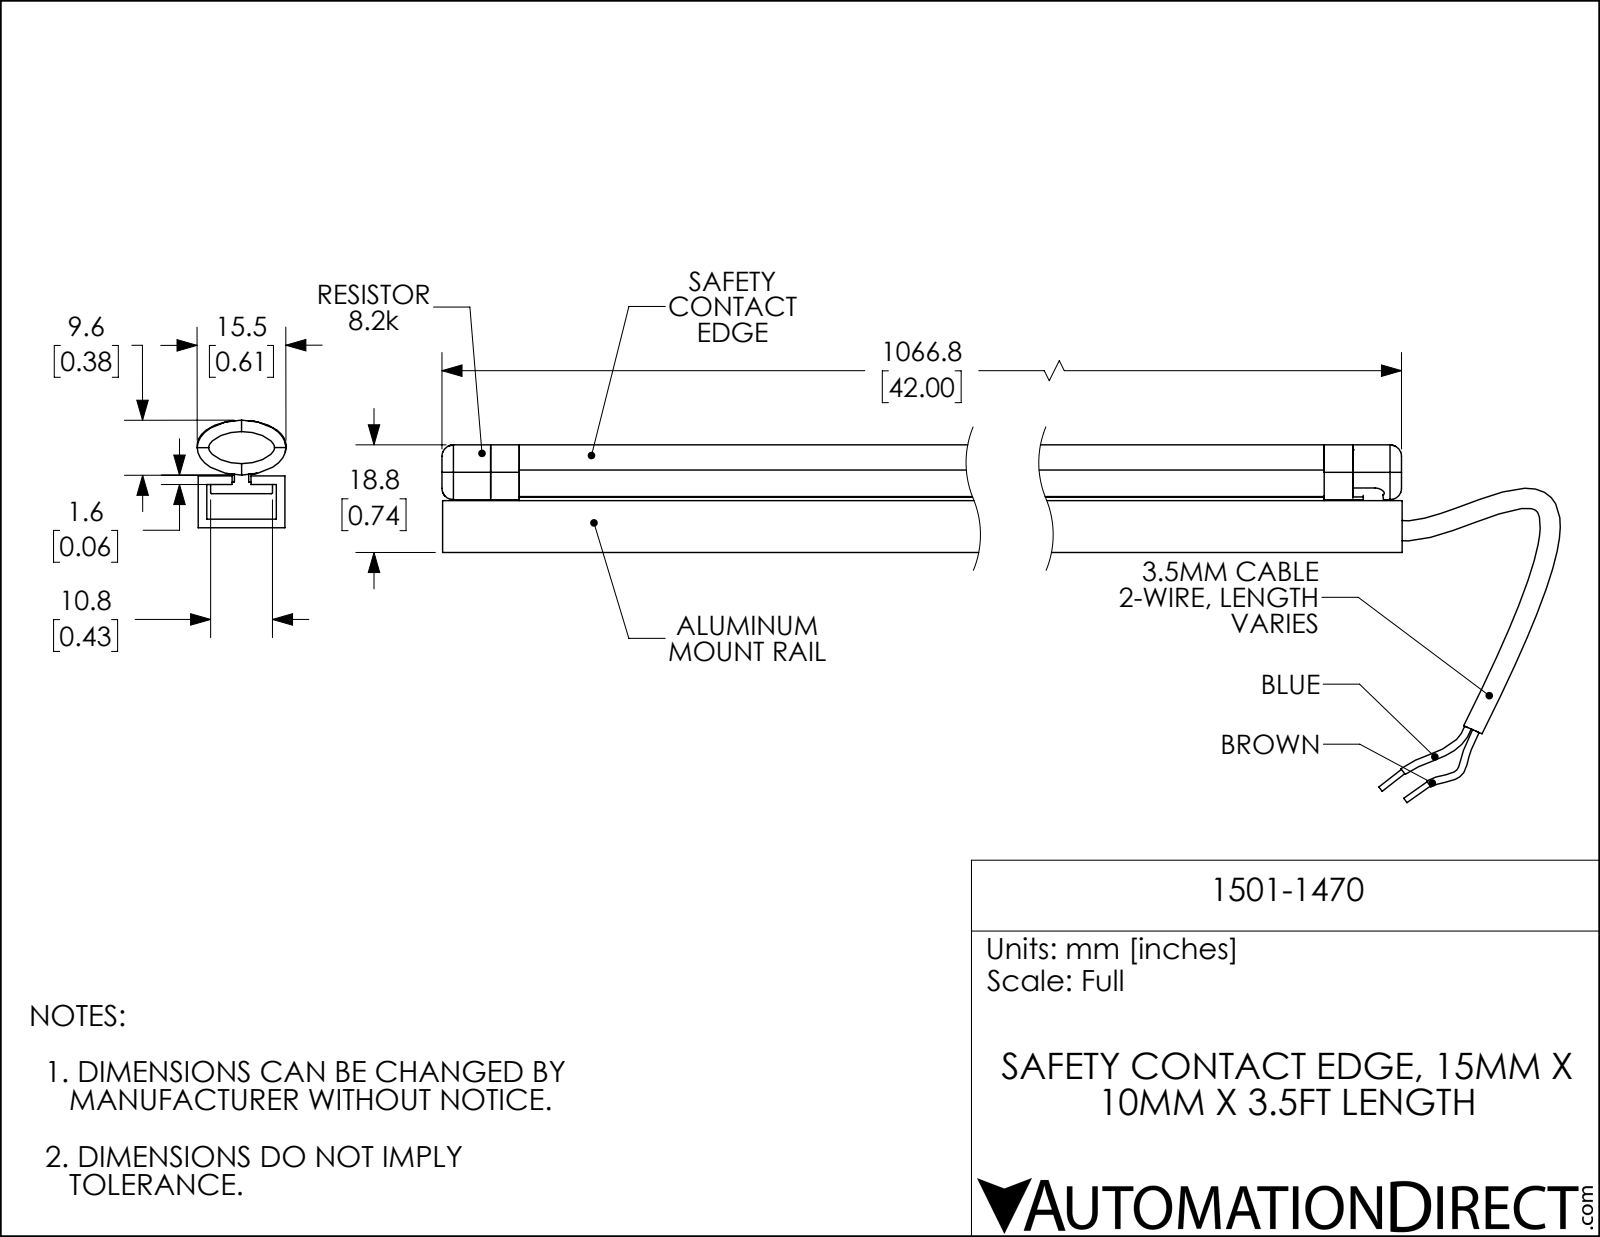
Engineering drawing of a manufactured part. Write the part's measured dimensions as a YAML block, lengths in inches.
part_name: "1501-1470"
step_written_by: "SolidWorks 2018 (AUTOMOTIVE_DESIGN)"
units: inches
bodies: {solids: 7, faces: 607, planar: 129, cylindrical: 154, other: 324}
overall_size: [43.092, 2.459, 0.611]
volume: 10.39
surface_area: 295.3
round_holes:
  - {diameter: 0.047, count: 4}
round_bosses_or_shafts:
  - {diameter: 0.037, count: 2}
partial_cylinders:
  - {radius: 0.004, count: 52}
  - {radius: 0.016, count: 15}
  - {radius: 0.012, count: 10}
  - {radius: 0.008, count: 7}
  - {radius: 0.02, count: 4}
  - {radius: 0.512, count: 4}
  - {radius: 0.008, count: 3}
  - {radius: 0.059, count: 3}
face_to_face_distances: [0.059, 0.297, 0.537, 0.356, 0.016, 0.122, 0.234, 0.175, 0.596, 0.238]
hole_center_spacings: [0.197, 0.196, 0.197]
